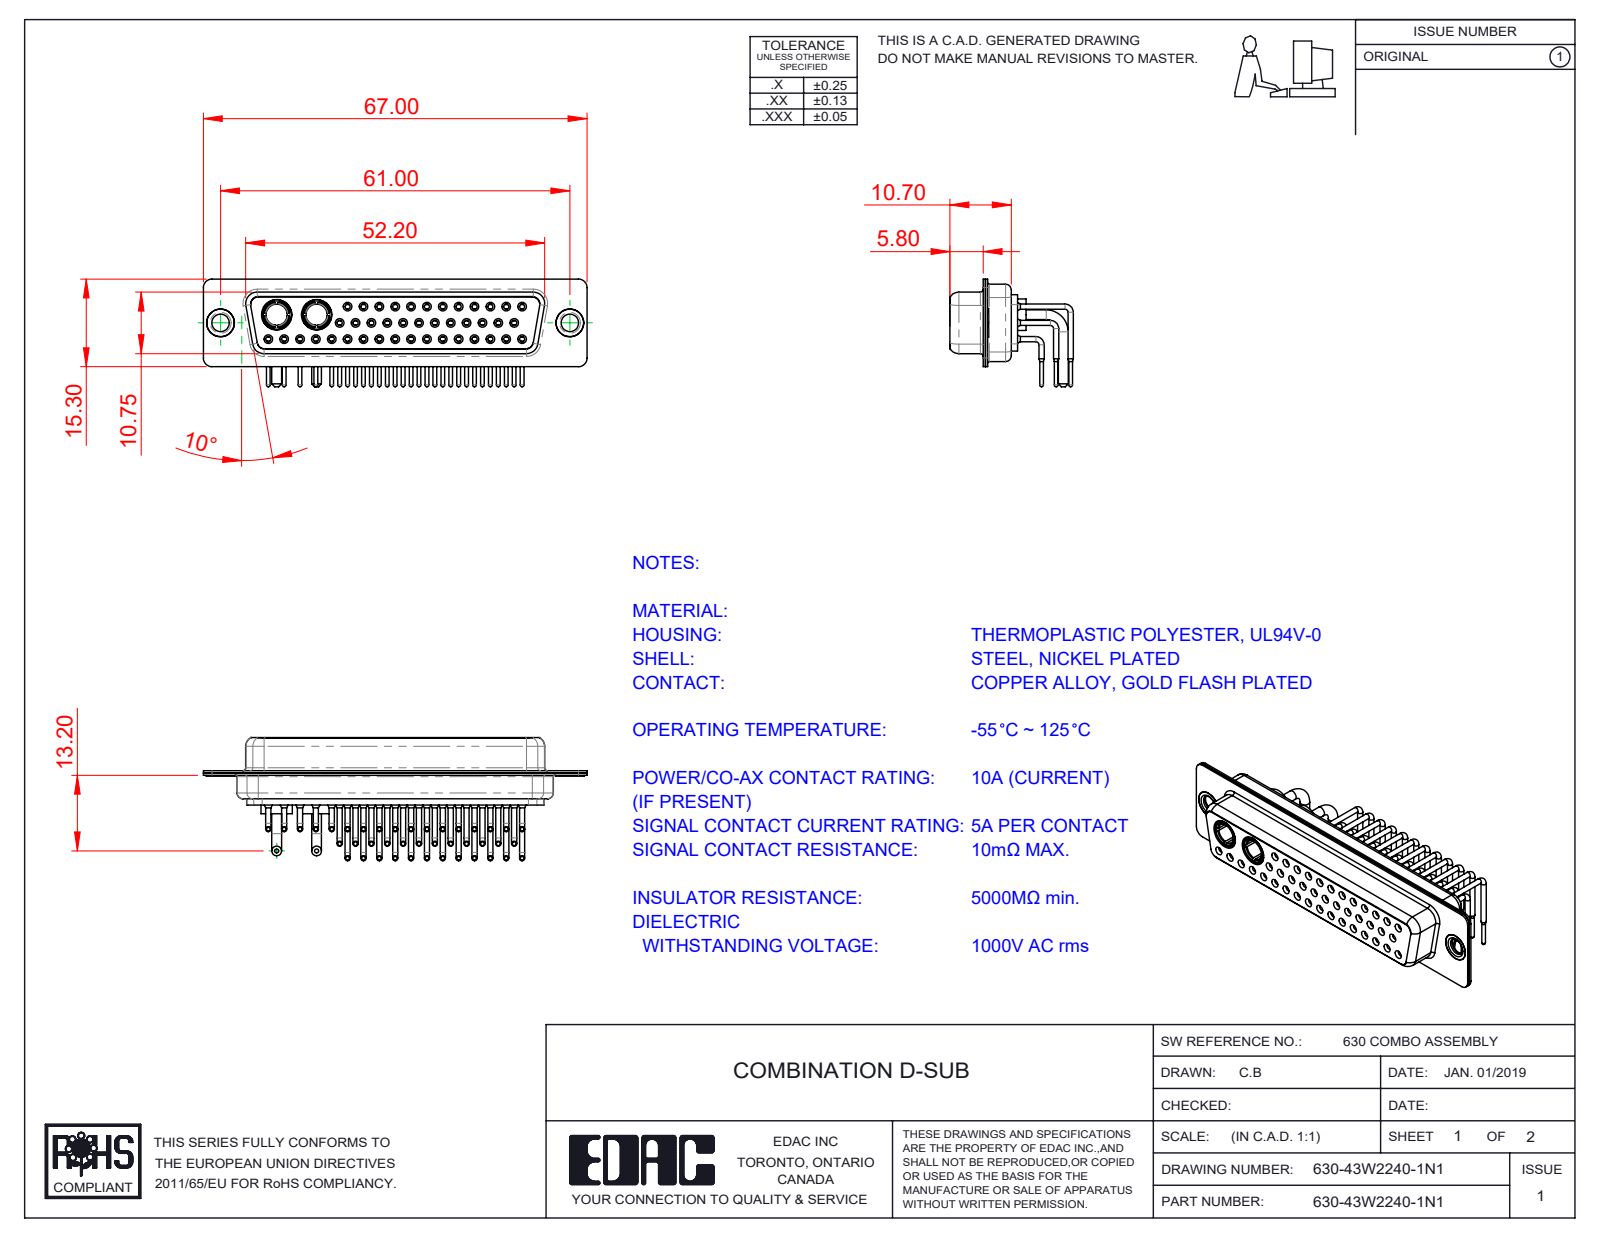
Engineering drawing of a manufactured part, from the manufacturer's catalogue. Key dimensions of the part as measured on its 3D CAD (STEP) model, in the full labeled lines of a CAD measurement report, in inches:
Part name (STEP PRODUCT): 630-43W2240-1N1; 630Combo Housing_43W2; 630Combo Contact Row 3; 630Combo Contact Row 1_50 Contacts (+5 more)
STEP written by: SolidWorks 2020 (CONFIG_CONTROL_DESIGN)
Units: inches
Bodies: 50 solids, 2582 faces (740 planar, 1114 cylindrical, 728 other)
Overall size (bounding box): 2.638 × 0.848 × 0.74
Volume: 0.429 in³ · Surface area: 24.21 in²
Round holes (diameter × count): ⌀0.035 ×41, ⌀0.043 ×41, ⌀0.059 ×41, ⌀0.079 ×41, ⌀0.063 ×29, ⌀0.067 ×12, ⌀0.191 ×4, ⌀0.12 ×2, ⌀0.146 ×2, ⌀0.157 ×2, ⌀0.159 ×2, ⌀0.209 ×2
Round bosses / shafts (diameter × count): ⌀0.035 ×41, ⌀0.026 ×41, ⌀0.063 ×12, ⌀0.067 ×4, ⌀0.217 ×2, ⌀0.205 ×2, ⌀0.197 ×2, ⌀0.195 ×2
Partial cylindrical surfaces — rounded edges, fillets, slot ends (radius × count): R0.059 ×16, R0.053 ×12, R0.079 ×12, R0.063 ×8, R0.01 ×4, R0.02 ×4, R0.024 ×4, R0.026 ×4
Main face-to-face distances: 0.016, 0.236, 0.22, 0.031, 0.444, 0.072, 0.228, 0.407, 0.465, 0.244
Hole centre spacings: 0.109, 0.124, 0.218, 0.327, 0.436, 0.545, 0.654, 0.763
